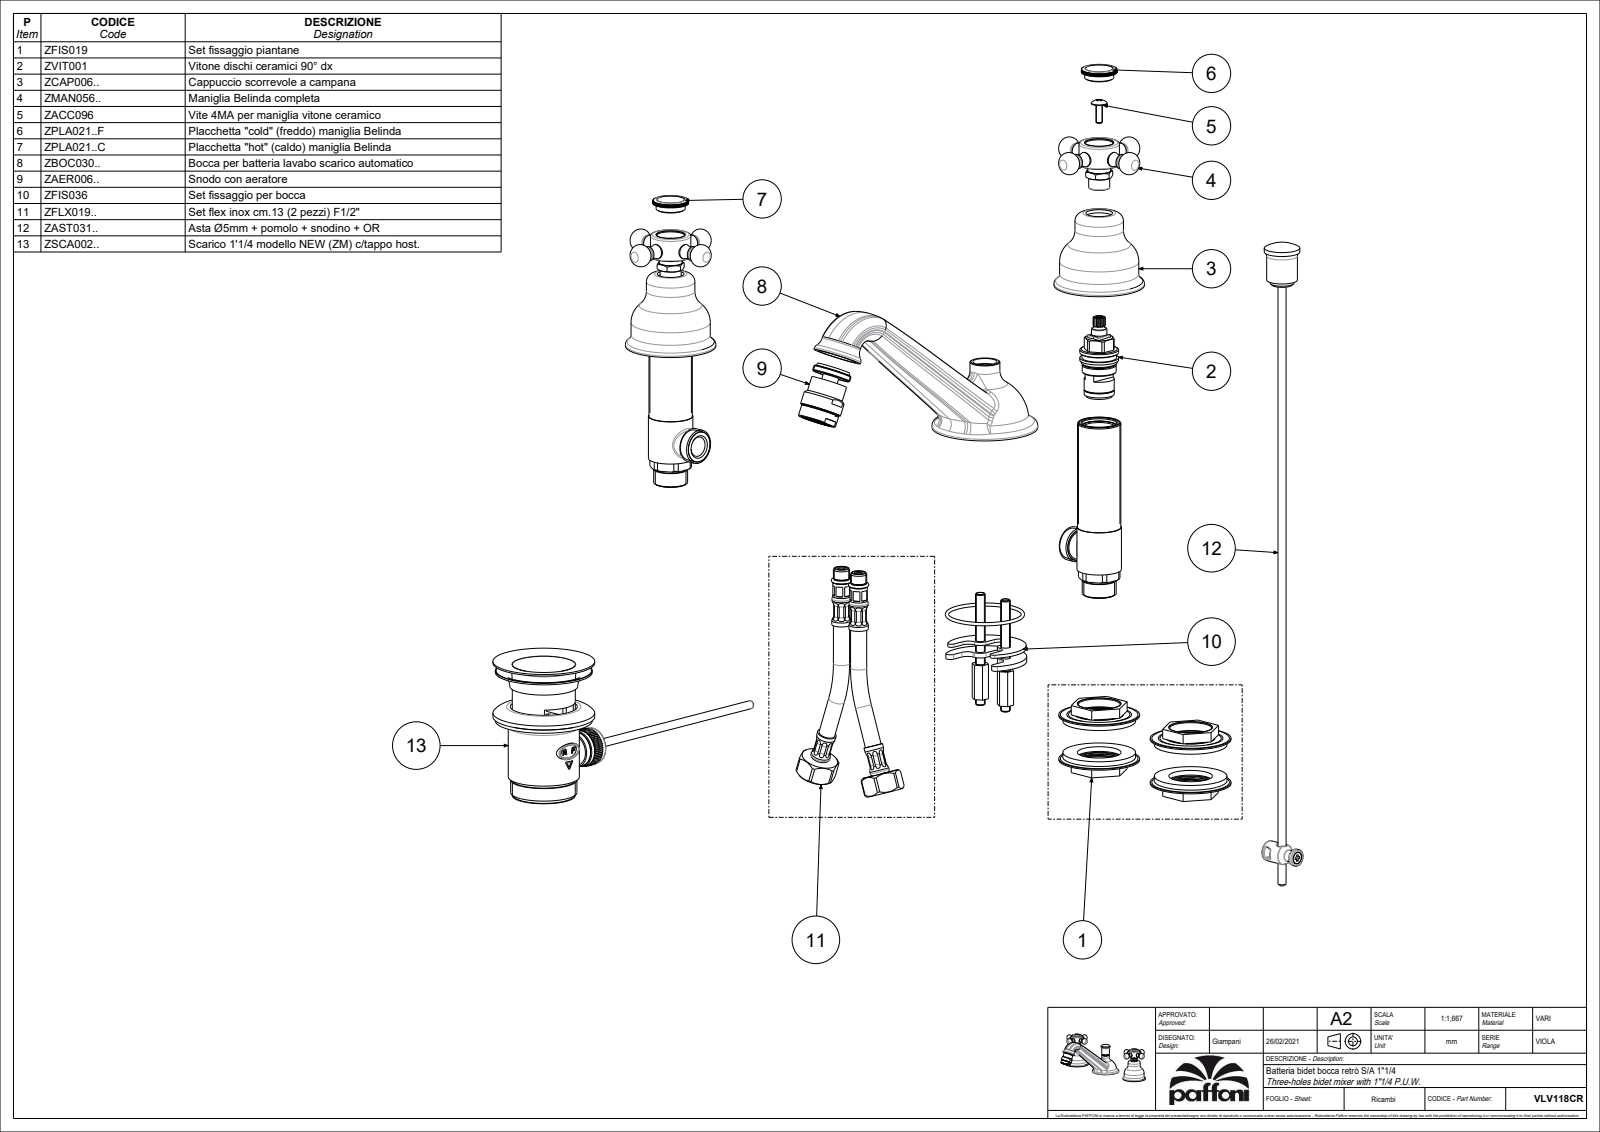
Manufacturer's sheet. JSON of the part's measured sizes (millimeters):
{"part_name": "VLV118CR", "step_written_by": "CREO PARAMETRIC BY PTC INC, 2020044 (CONFIG_CONTROL_DESIGN)", "units": "millimeters", "bodies": {"solids": 3, "faces": 1013, "planar": 450, "cylindrical": 298, "other": 265}, "overall_size": [264.07, 184.84, 94.3], "volume_mm3": 311353, "surface_area_mm2": 55913, "round_bosses_or_shafts": [[9, 3], [7, 3], [55, 2], [49, 2], [28, 2], [25, 2], [24, 2], [14, 2]], "partial_cylinders_radius": [[11, 2]], "face_to_face_distances": [57.2, 3, 28.69, 25.69, 46.5, 10.7, 15, 42.8, 3.7, 14.4]}
